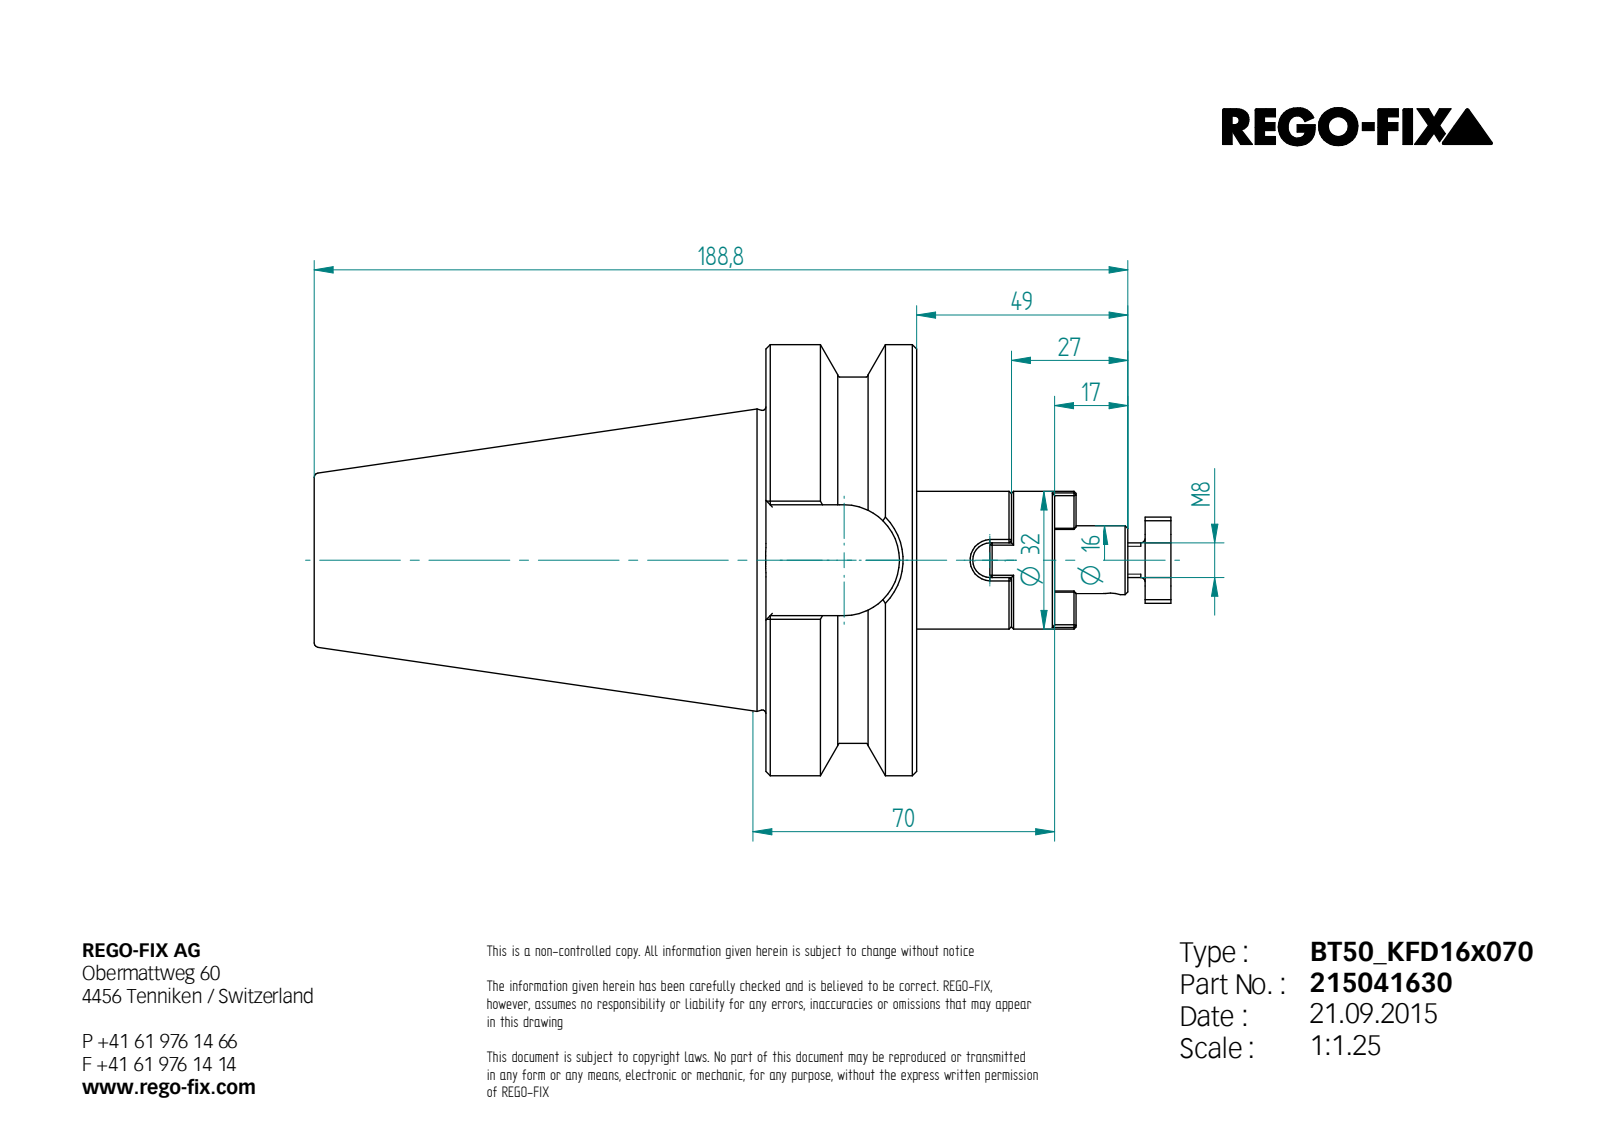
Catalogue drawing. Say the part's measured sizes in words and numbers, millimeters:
Its 3-D file was written by "Unknown (AUTOMOTIVE_DESIGN)". It is 3 solids with 207 faces: 118 planar, 35 cylindrical and 54 other. Overall it measures 198.8 by 100 by 100 millimeters. Its volume is 473 331 cubic millimeters and its surface area 63 050 square millimeters. Round holes: 1 of diameter 6.65, 1 of diameter 8.4, 1 of diameter 16, 1 of diameter 20.75, 1 of diameter 25. Round bosses or shafts: 1 of diameter 100, 1 of diameter 85, 1 of diameter 32, 1 of diameter 15.6, 1 of diameter 8. Partial cylindrical surfaces (rounded edges, fillets, slot ends): 6 of radius 2, 4 of radius 0.5, 1 of radius 4, 1 of radius 10, 1 of radius 12.85. The main face-to-face distances are 35, 22, 57, 70.7, 104.8, 139.8, 161.8, 32, 10, 171.8.
